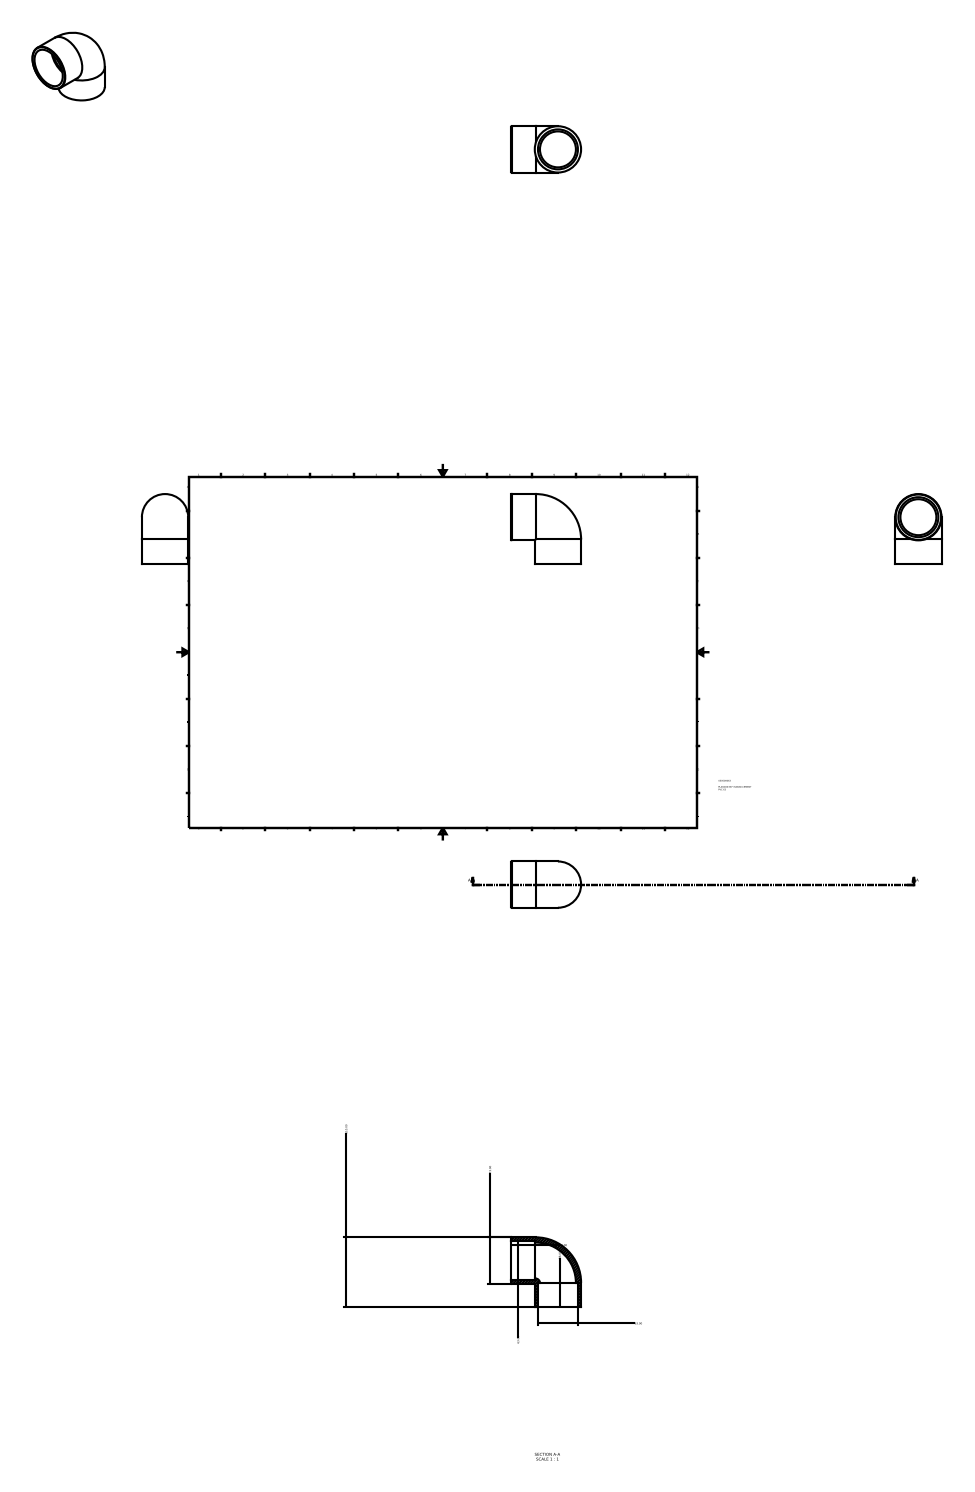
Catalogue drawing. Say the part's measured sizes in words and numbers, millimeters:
The part is named "050500063". Its 3-D file was written by "Autodesk Inventor 2015 (AUTOMOTIVE_DESIGN)". It is 1 solid with 11 faces: 4 planar, 4 cylindrical and 3 other. Overall it measures 110 by 110 by 73 millimeters. Its volume is 177 963 cubic millimeters and its surface area 58 519 square millimeters. Round holes: 2 of diameter 63. Round bosses or shafts: 2 of diameter 73. The main face-to-face distances are 38.
